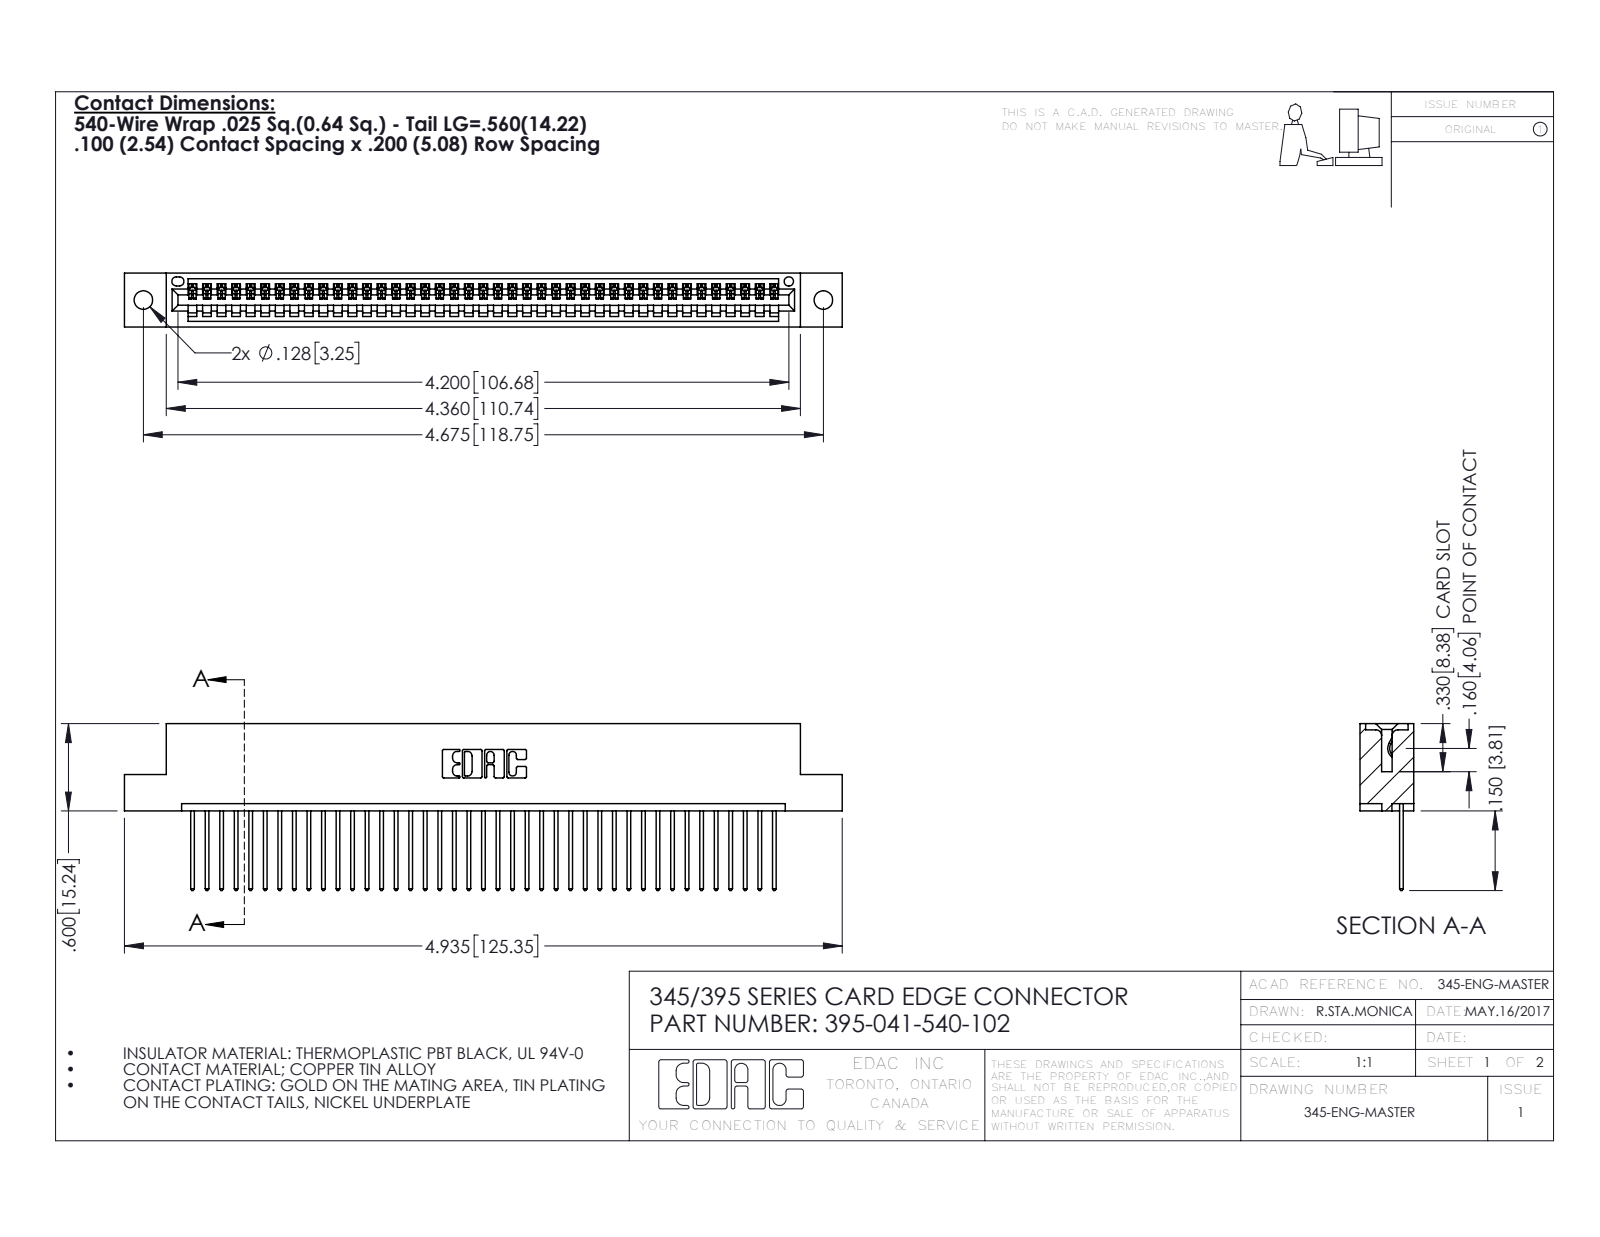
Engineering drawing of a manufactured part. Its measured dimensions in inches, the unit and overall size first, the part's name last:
Units: inches
Overall size (bounding box): 4.935 × 1.147 × 0.37
Round holes (diameter × count): ⌀0.128 ×2, ⌀0.064 ×1
Partial cylindrical surfaces — rounded edges, fillets, slot ends (radius × count): R0.006 ×82, R0.01 ×82, R0.01 ×22, R0.007 ×6, R0.031 ×6, R0.026 ×3, R0.031 ×2, R0.04 ×2
Main face-to-face distances: 0.298, 0.072, 0.37, 0.098, 0.272, 0.025, 0.2, 0.225, 0.149, 0.072
Hole centre spacings: 0.27, 4.439, 4.675
Volume: 0.727 in³ · Surface area: 24.72 in²
Bodies: 42 solids, 2504 faces (1720 planar, 784 cylindrical, 0 other)
Part name (STEP PRODUCT): 395-041-540-102; 345 Part_Flush Mounting Lugs - 0.128 Dia; 345-292-001_345-293-140
STEP written by: SolidWorks 2016 (CONFIG_CONTROL_DESIGN)
